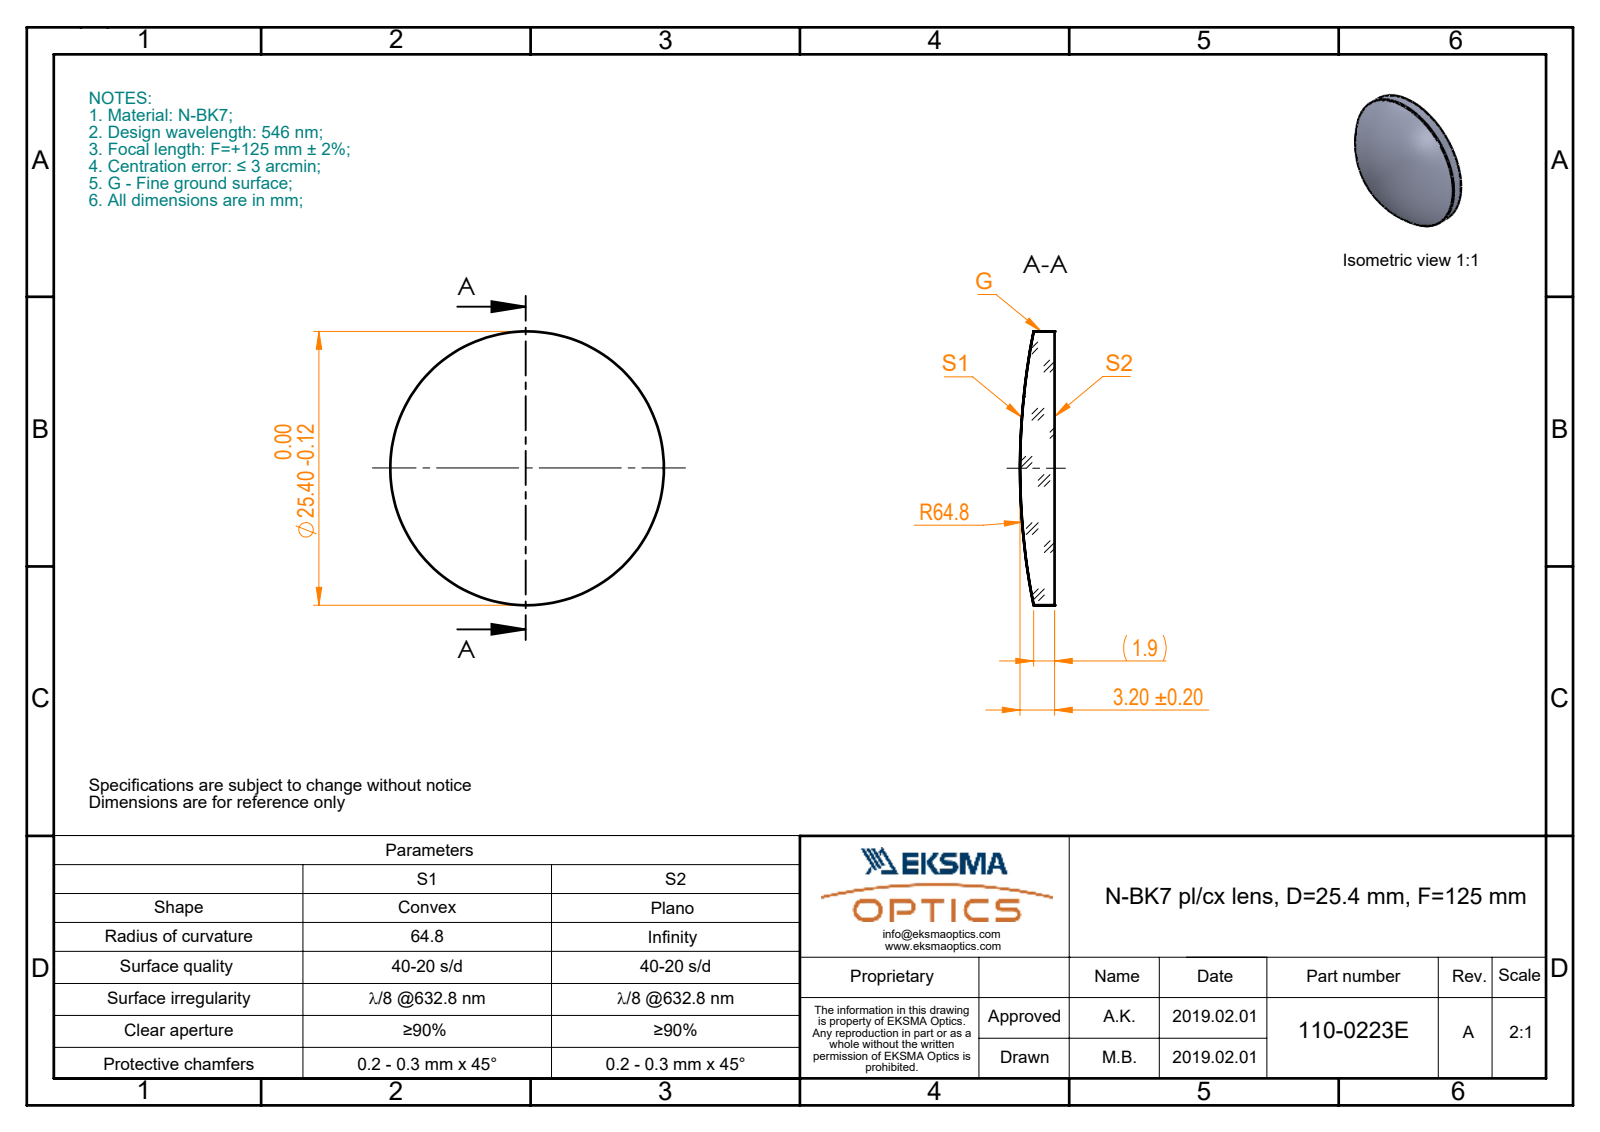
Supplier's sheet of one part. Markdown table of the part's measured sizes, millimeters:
| quantity | value |
| --- | --- |
| part name | 110-0223E BK7 pl-cx 25.4 F125 |
| STEP written by | SolidWorks 2017 (CONFIG_CONTROL_DESIGN) |
| units | millimeters |
| bodies | 1 solid, 5 faces (1 planar, 2 cylindrical, 2 other) |
| overall size | 25.4 × 25.4 × 3.2 |
| volume | 1 304 mm³ |
| surface area | 1 174 mm² |
| round bosses / shafts (diameter × count) | 25.4 × 1 |
